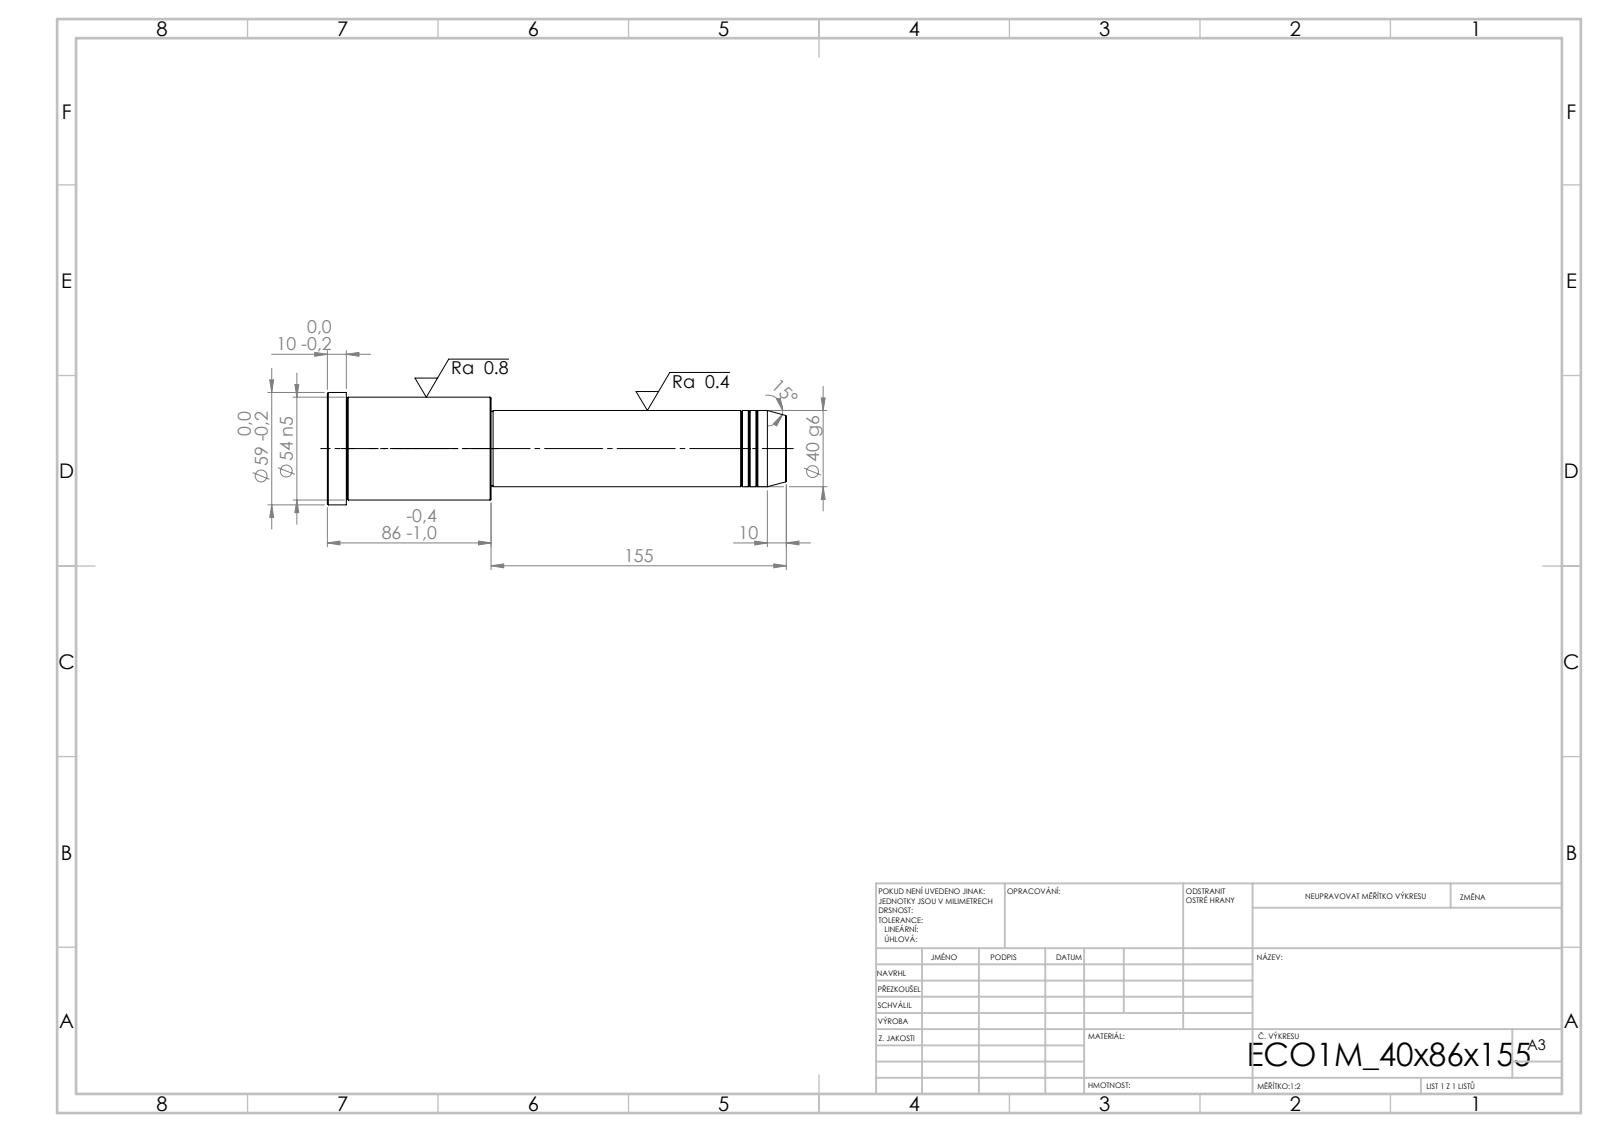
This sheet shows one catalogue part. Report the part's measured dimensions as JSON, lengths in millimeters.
{"step_written_by": "SolidWorks 2019 (CONFIG_CONTROL_DESIGN)", "units": "millimeters", "bodies": {"solids": 1, "faces": 43, "planar": 5, "cylindrical": 14, "other": 24}, "overall_size": [241, 59, 59], "volume_mm3": 394245, "surface_area_mm2": 39639, "round_bosses_or_shafts": [[59, 1], [54, 1], [40, 1], [39, 1]], "face_to_face_distances": [86, 155, 241, 231, 76, 10, 154, 1, 77, 87]}
